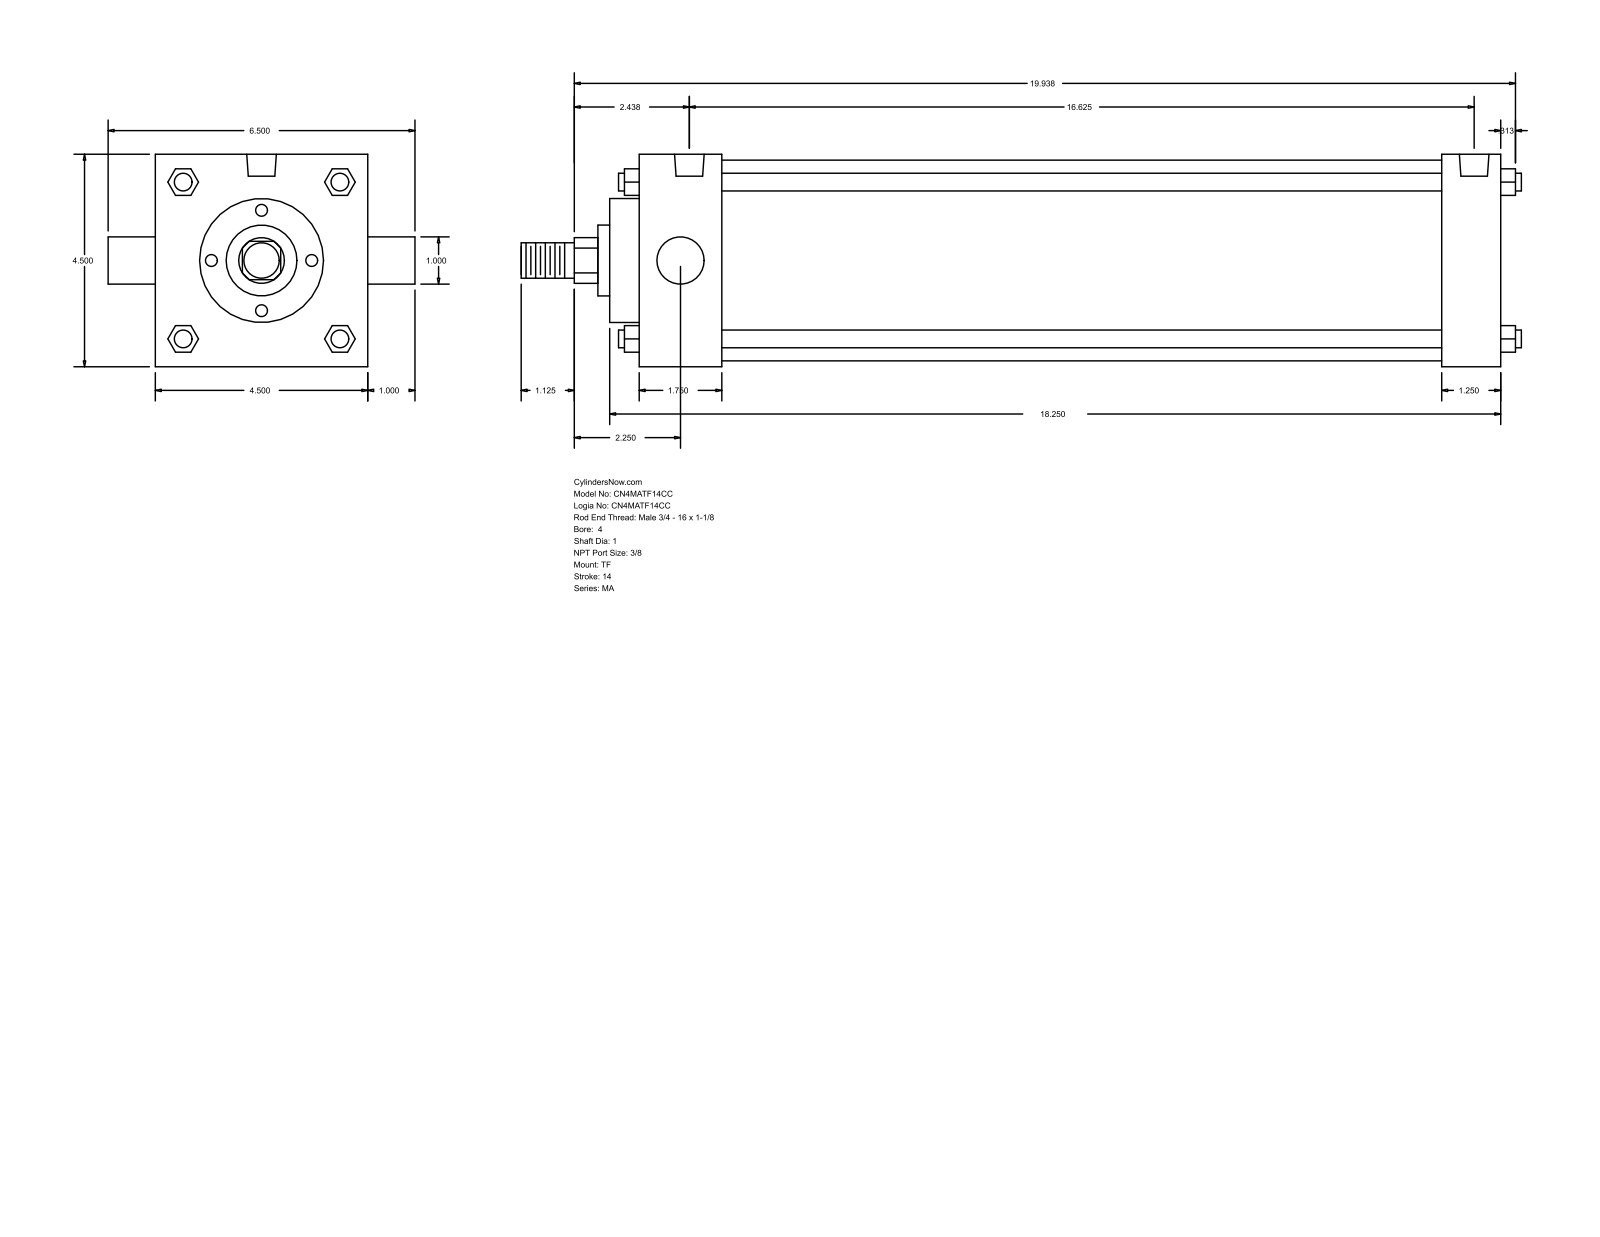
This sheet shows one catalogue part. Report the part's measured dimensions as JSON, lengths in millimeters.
{"part_name": "MA_TF__0400_1", "step_written_by": "GSSL Pune (CONFIG_CONTROL_DESIGN)", "units": "millimeters", "bodies": {"solids": 0, "faces": 122, "planar": 93, "cylindrical": 29, "other": 0}, "overall_size": [538.16, 165.1, 114.3], "round_holes": [[11.11, 3], [15.93, 2]], "round_bosses_or_shafts": [[9.53, 4], [25.4, 2], [107.95, 1], [66.67, 1], [38.1, 1], [19.05, 1]], "partial_cylinders_radius": [[12.29, 1]], "face_to_face_distances": [114.3, 463.56, 431.81, 31.75, 44.46, 387.35, 419.1, 15.87, 60.33, 447.68], "hole_center_spacings": [4.76, 417.52, 412.76, 422.28]}
